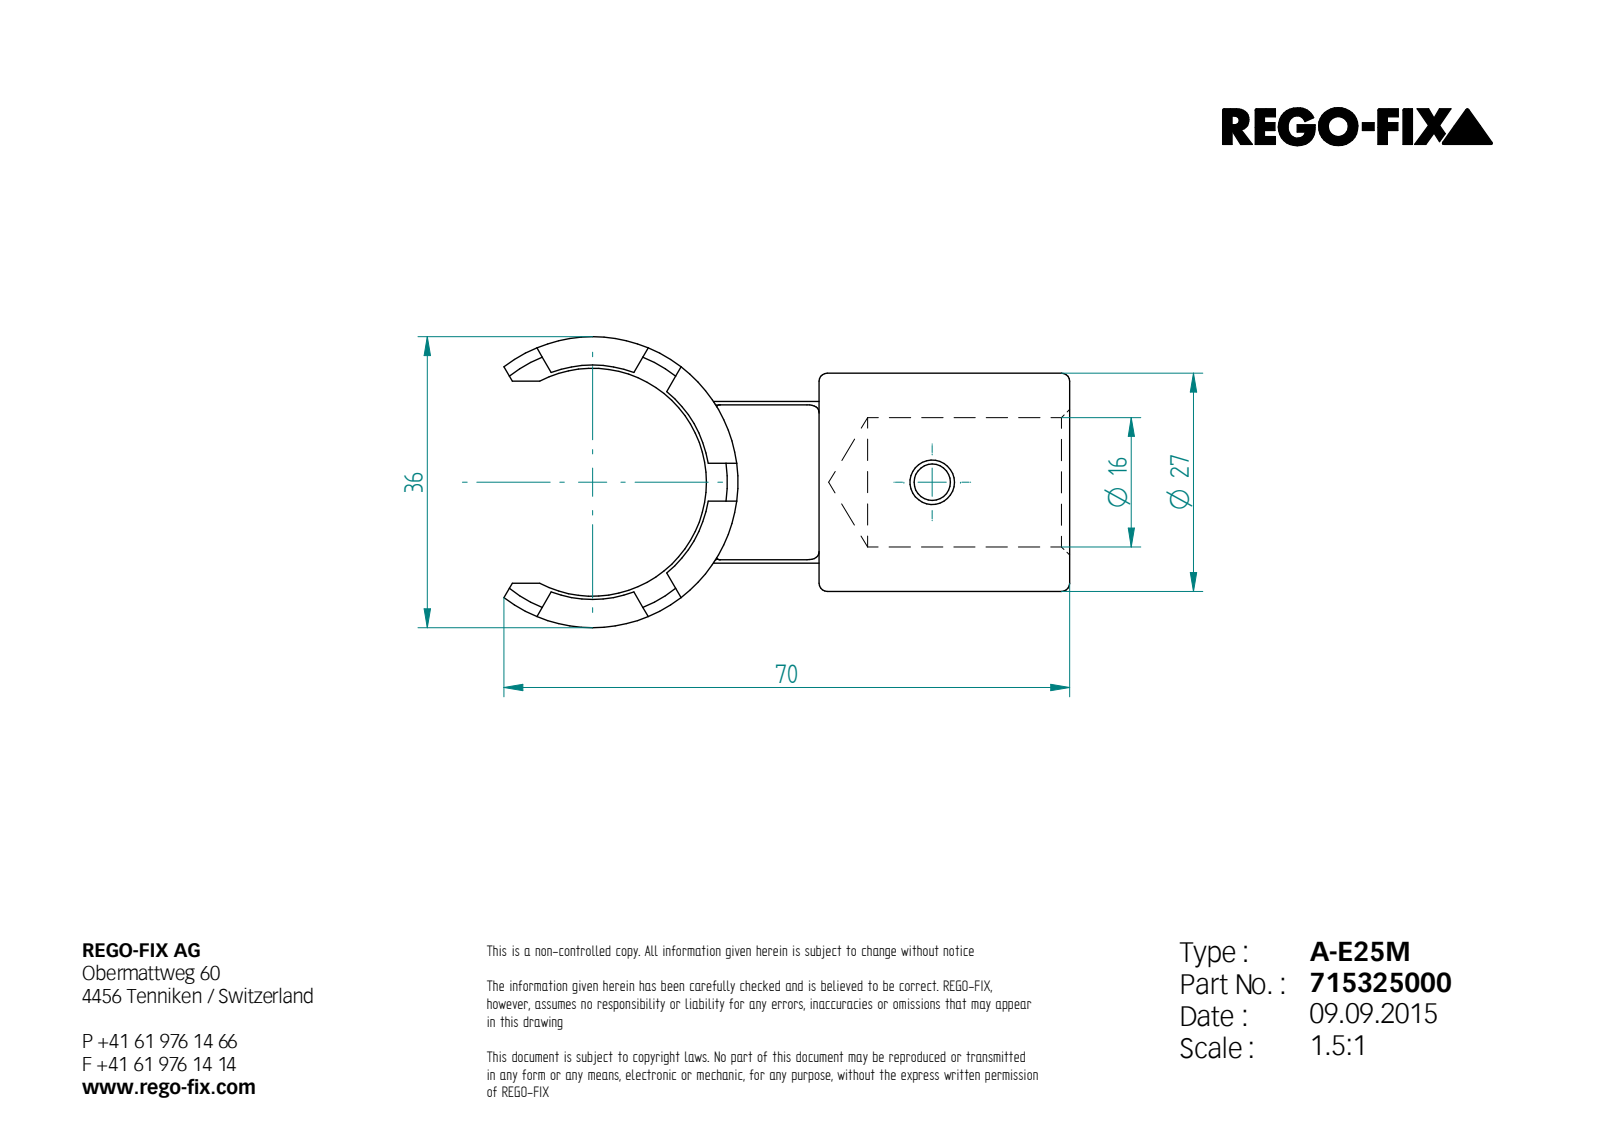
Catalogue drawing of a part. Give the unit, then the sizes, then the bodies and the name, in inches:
Units: inches
Overall size (bounding box): 2.756 × 1.417 × 1.063
Round holes (diameter × count): ⌀0.177 ×1, ⌀0.217 ×1, ⌀0.63 ×1
Round bosses / shafts (diameter × count): ⌀1.063 ×1
Partial cylindrical surfaces — rounded edges, fillets, slot ends (radius × count): R0.059 ×2, R0.197 ×2, R0.555 ×1, R0.709 ×1
Main face-to-face distances: 0.157, 1.22, 0.315, 0.185, 0.984, 0.551, 0.394, 0.236, 0.4, 0.585
Volume: 0.946 in³ · Surface area: 11.65 in²
Bodies: 1 solid, 43 faces (25 planar, 11 cylindrical, 7 other)
STEP written by: Unknown (AUTOMOTIVE_DESIGN)
